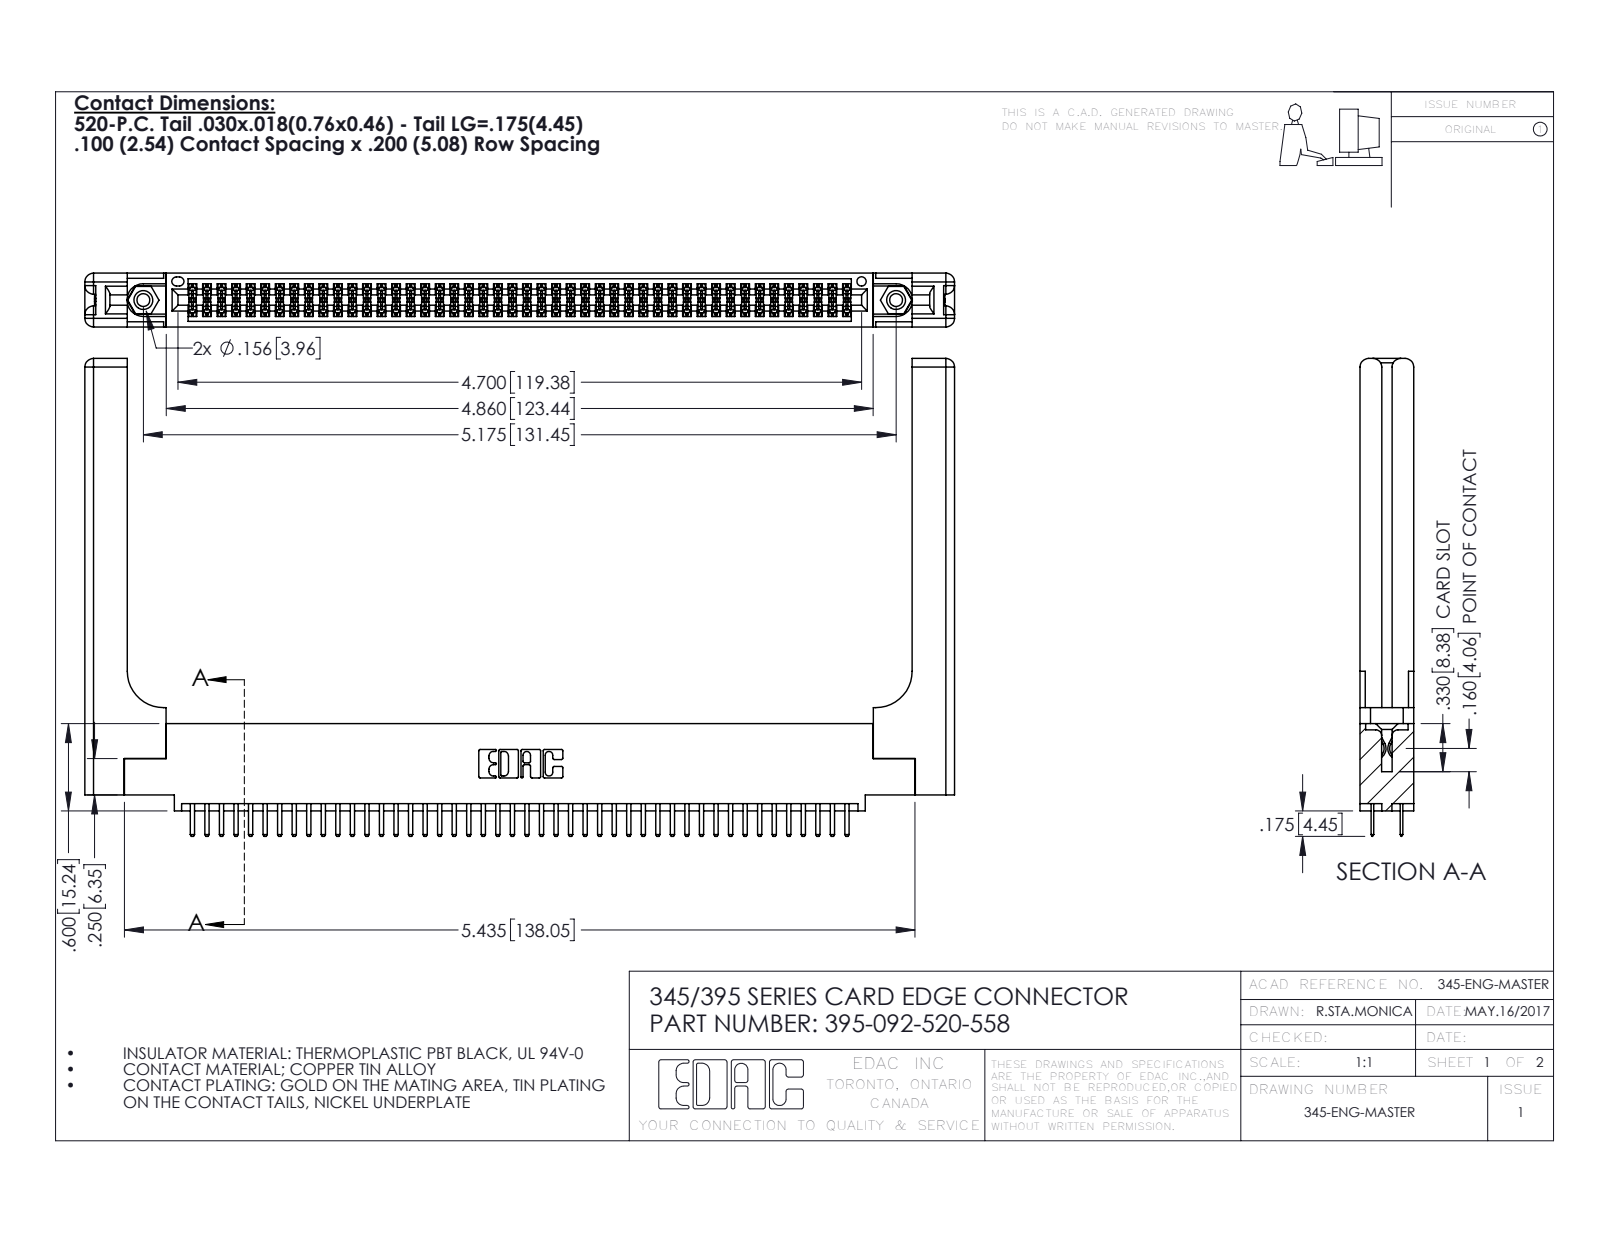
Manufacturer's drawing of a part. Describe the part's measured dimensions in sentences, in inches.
The part is named "345-250-001_345-250-001-102; 345 Part_0.110 Offset - 0.156 Dia-TH; 345-292-001_345-293-120; 345-220-058_345-220-058 (+1 more)". Its 3-D file was written by "SolidWorks 2016 (CONFIG_CONTROL_DESIGN)". It is 97 solids with 5354 faces: 3452 planar, 1842 cylindrical and 60 other. Overall it measures 5.979 by 3.285 by 0.37 inches. Its volume is 1.413 cubic inches and its surface area 41.6 square inches. Round holes: 2 of diameter 0.089, 2 of diameter 0.125, 2 of diameter 0.156, 1 of diameter 0.064. Round bosses or shafts: 2 of diameter 0.155. Partial cylindrical surfaces (rounded edges, fillets, slot ends): 138 of radius 0.006, 96 of radius 0.01, 22 of radius 0.01, 16 of radius 0.06, 6 of radius 0.007, 6 of radius 0.031, 3 of radius 0.026, 2 of radius 0.014. The main face-to-face distances are 0.072, 0.37, 0.298, 0.2, 0.098, 0.272, 0.025, 0.225, 0.148, 0.15. The hole center spacings are 0.27, 4.939, 5.175.
